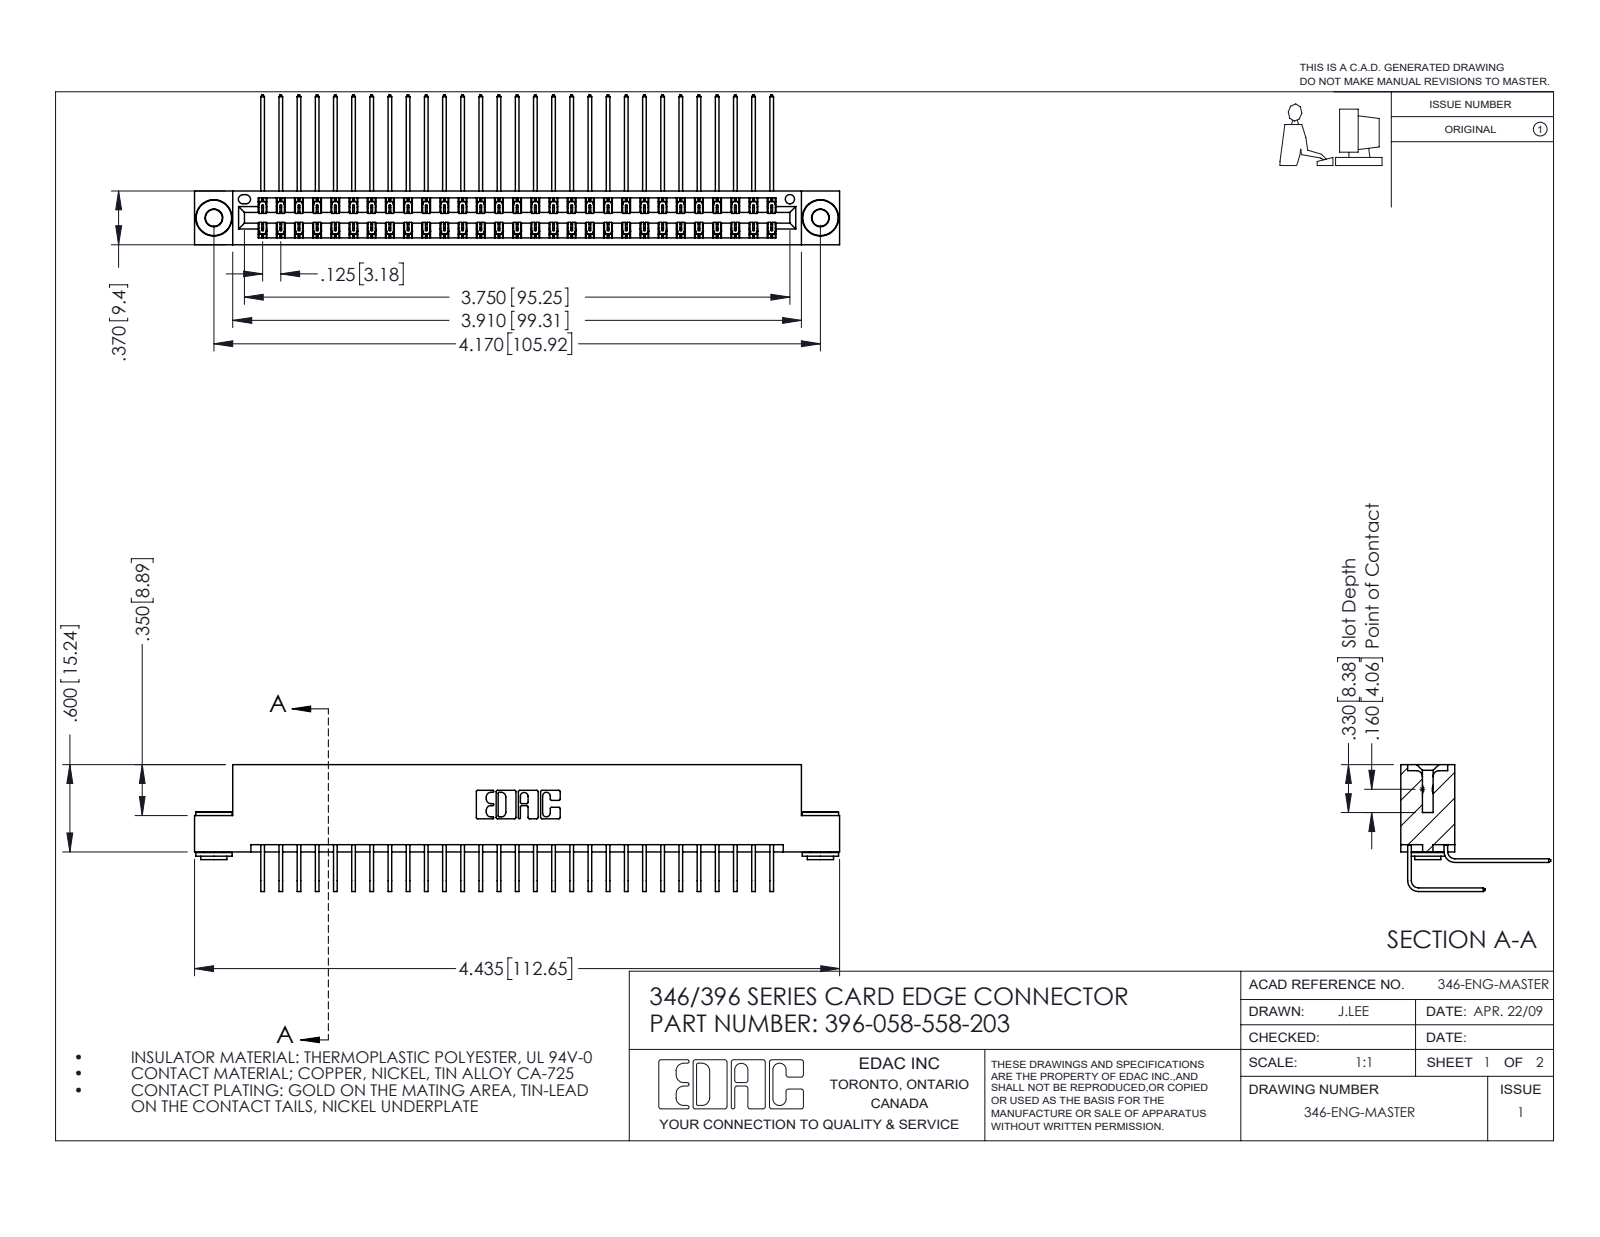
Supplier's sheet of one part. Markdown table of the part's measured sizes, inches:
| quantity | value |
| --- | --- |
| part name | 345-292-001_558 Tail - 2; 345-292-001_558 559 Tail - 1; 396-058-558-203; 346 Part_Flush Mounting Lugs - 0.156 Dia-TH (+1 more) |
| STEP written by | SolidWorks 2016 (CONFIG_CONTROL_DESIGN) |
| units | inches |
| bodies | 61 solids, 3292 faces (2232 planar, 1052 cylindrical, 8 other) |
| overall size | 4.435 × 1.03 × 0.873 |
| volume | 0.686 in³ |
| surface area | 26.45 in² |
| round holes (diameter × count) | 0.116 × 2, 0.156 × 2, 0.064 × 1 |
| round bosses / shafts (diameter × count) | 0.25 × 2, 0.18 × 2, 0.136 × 2 |
| partial cylindrical surfaces (radius × count) | 0.006 × 87, 0.01 × 22, 0.007 × 6, 0.031 × 6, 0.026 × 3, 0.014 × 2, 0.022 × 2, 0.024 × 2 |
| main face-to-face distances | 0.322, 0.048, 0.025, 0.25, 0.37, 0.298, 0.072, 0.275, 0.148, 0.222 |
| hole center spacings | 0.246, 3.962, 4.17 |
